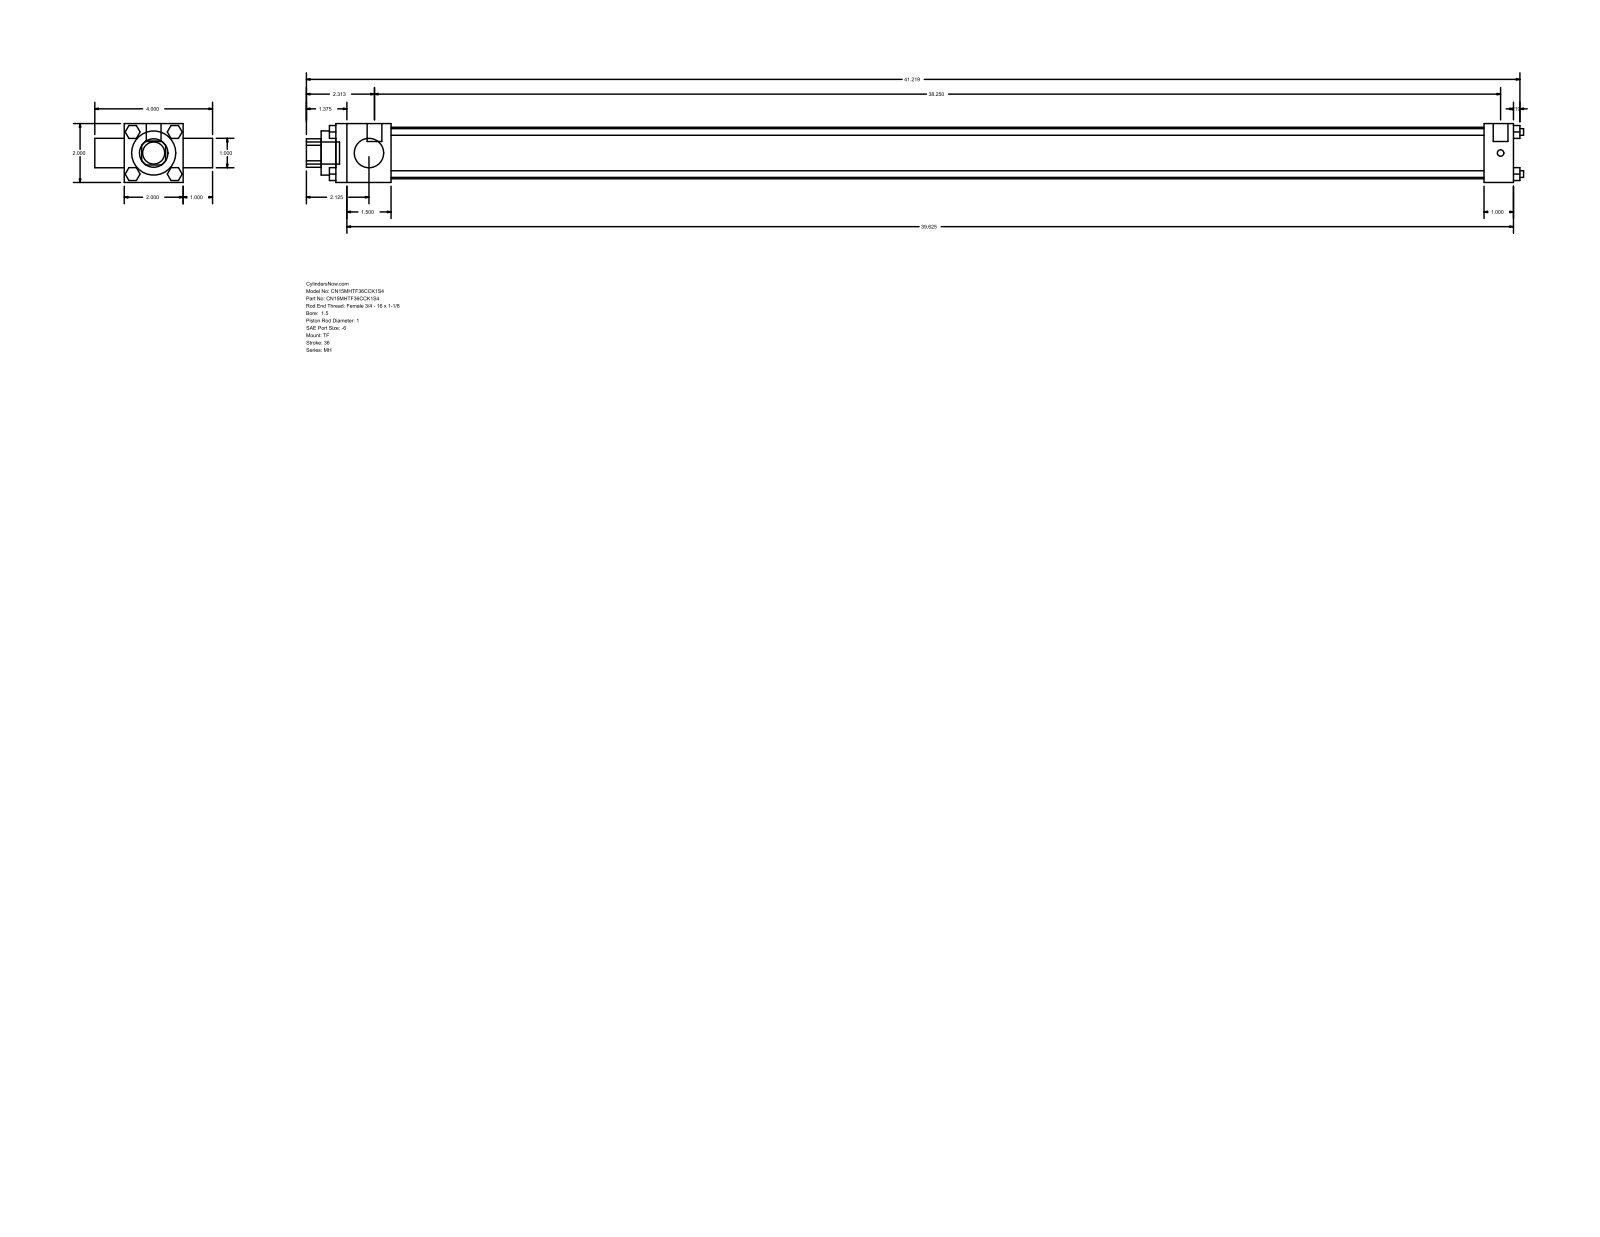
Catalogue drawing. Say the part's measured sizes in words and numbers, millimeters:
The part is named "MH_TF__0150_1". Its 3-D file was written by "GSSL Pune (CONFIG_CONTROL_DESIGN)". It is 0 solids with 120 faces: 92 planar, 28 cylindrical and 0 other. Overall it measures 1050.13 by 101.6 by 50.8 millimeters. Round holes: 2 of diameter 25.4, 1 of diameter 38.1, 1 of diameter 44.45. Round bosses or shafts: 4 of diameter 5.71, 3 of diameter 5.56, 2 of diameter 12.7, 1 of diameter 19.05. Partial cylindrical surfaces (rounded edges, fillets, slot ends): 1 of radius 12.29. The main face-to-face distances are 50.8, 25.4, 1016, 76.2, 47.63, 968.37, 990.6, 942.97, 1021.56, 12.7.
